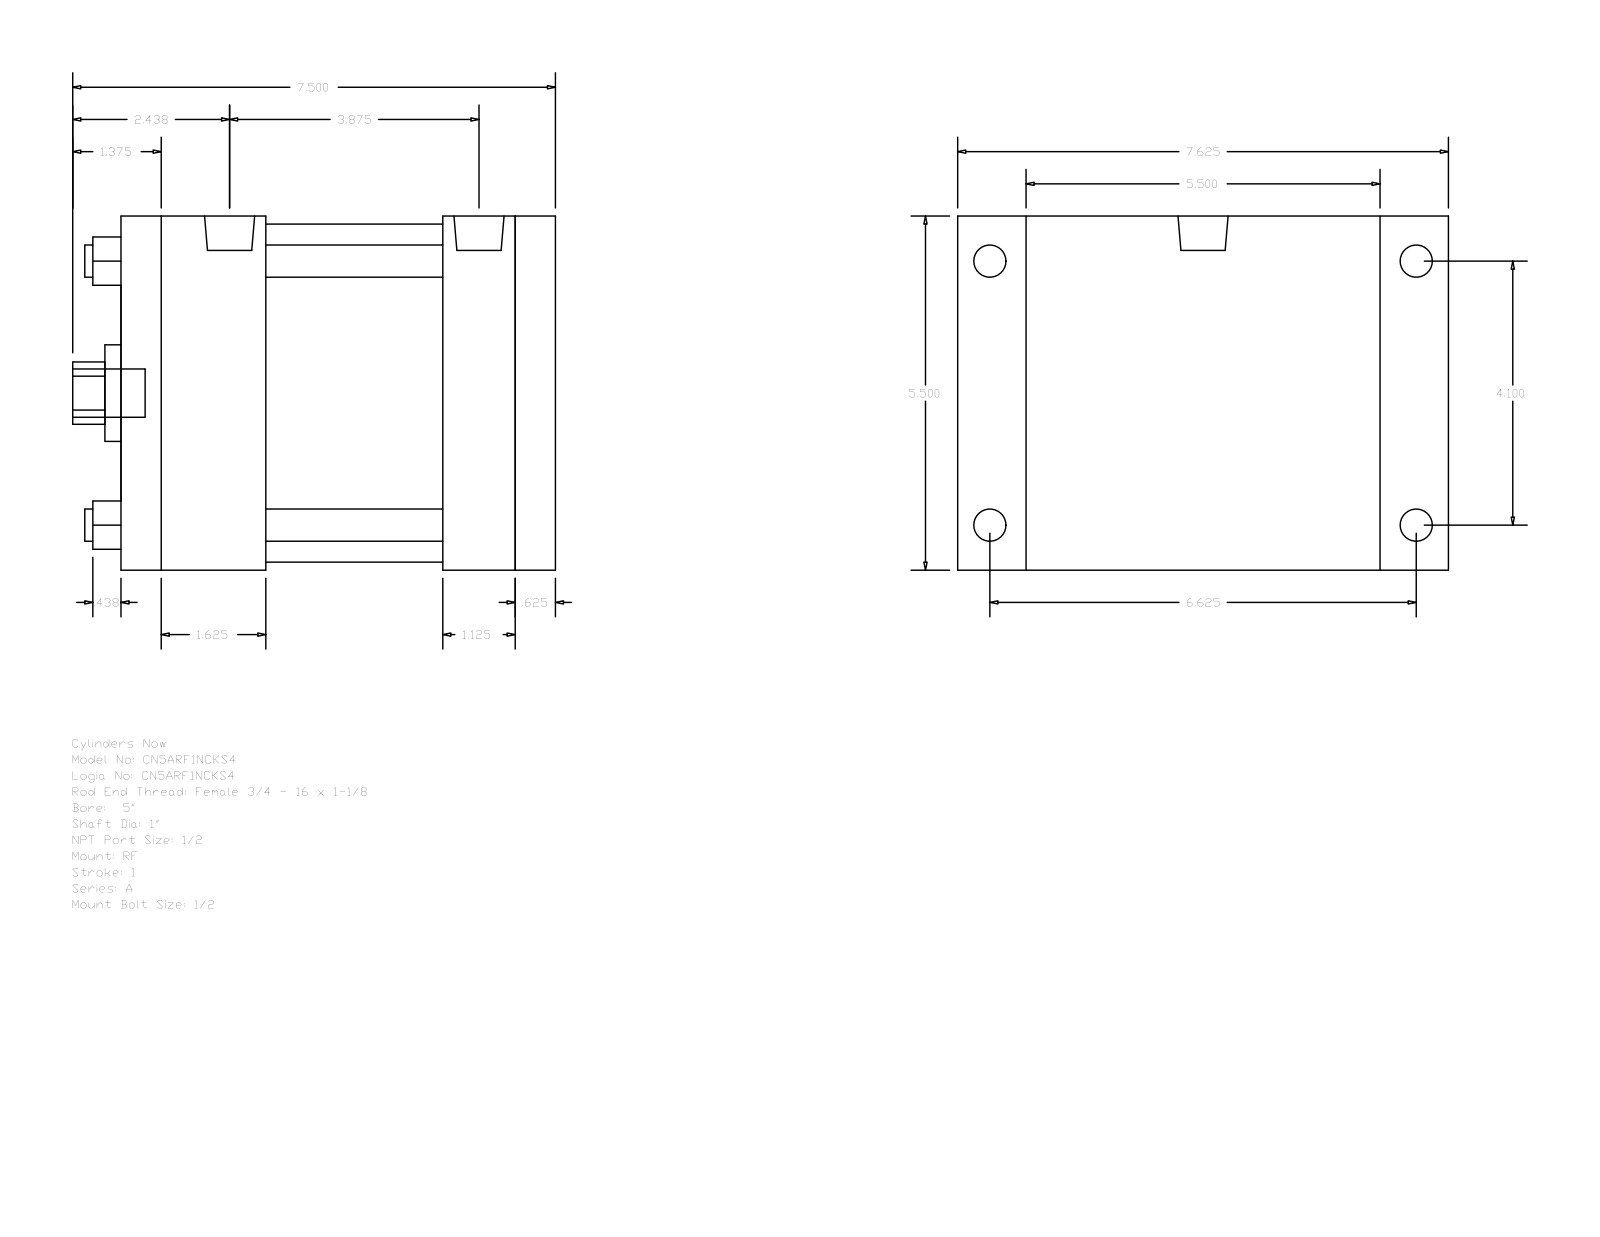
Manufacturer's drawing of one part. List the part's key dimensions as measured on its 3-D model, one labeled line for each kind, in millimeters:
Part name (STEP PRODUCT): A_RF__0500_1
STEP written by: GSSL Pune (CONFIG_CONTROL_DESIGN)
Units: millimetres
Bodies: 0 solids, 92 faces (64 planar, 28 cylindrical, 0 other)
Overall size (bounding box): 193.68 × 190.5 × 139.7
Round holes (diameter × count): ⌀12.7 ×4, ⌀25.4 ×1, ⌀38.1 ×1, ⌀133.35 ×1
Round bosses / shafts (diameter × count): ⌀12.7 ×4, ⌀8.73 ×4, ⌀19.77 ×2, ⌀19.05 ×1
Partial cylindrical surfaces — rounded edges, fillets, slot ends (radius × count): R12.29 ×1
Main face-to-face distances: 139.7, 171.45, 155.57, 15.88, 28.57, 57.15, 98.42, 114.3, 127, 69.85
Hole centre spacings: 73.64, 104.14, 147.28
